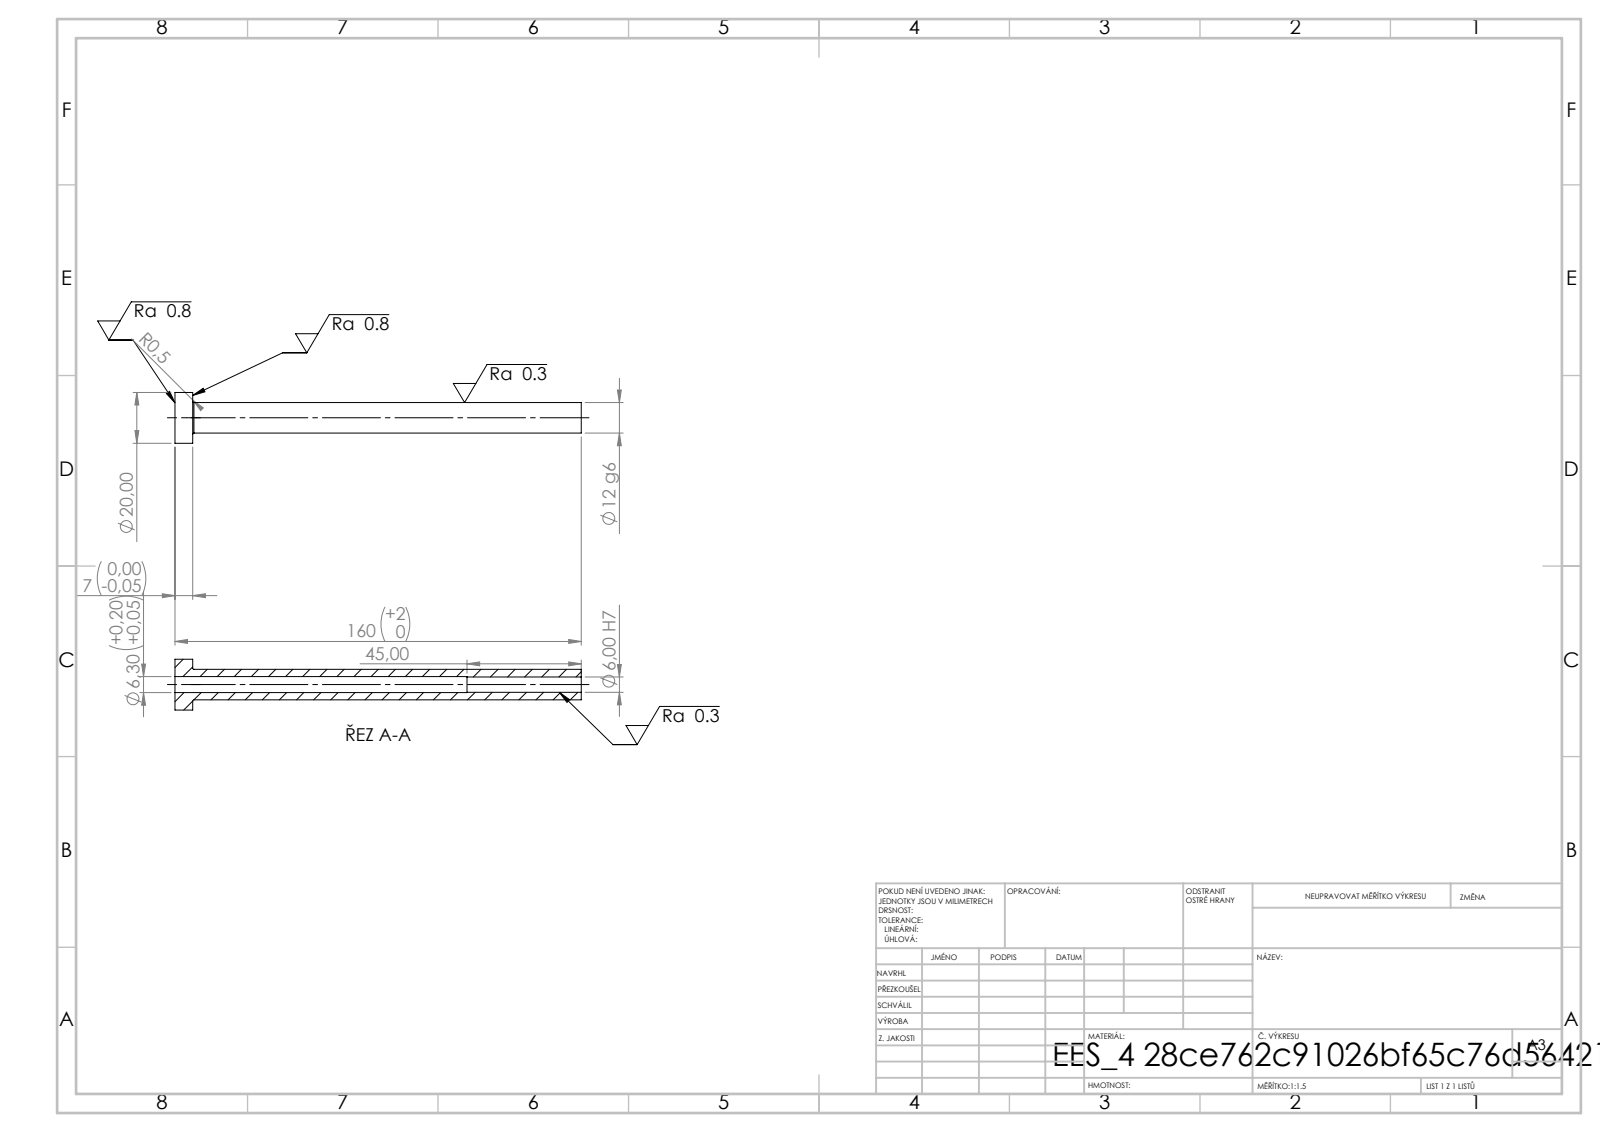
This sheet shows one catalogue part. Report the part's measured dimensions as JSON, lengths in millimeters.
{"step_written_by": "SolidWorks 2019 (CONFIG_CONTROL_DESIGN)", "units": "millimeters", "bodies": {"solids": 1, "faces": 14, "planar": 4, "cylindrical": 8, "other": 2}, "overall_size": [160, 20, 20], "volume_mm3": 14648, "surface_area_mm2": 9896, "round_holes": [[6, 1], [6.3, 1]], "round_bosses_or_shafts": [[20, 1], [12, 1]], "face_to_face_distances": [7, 160, 153, 115, 108, 45]}
